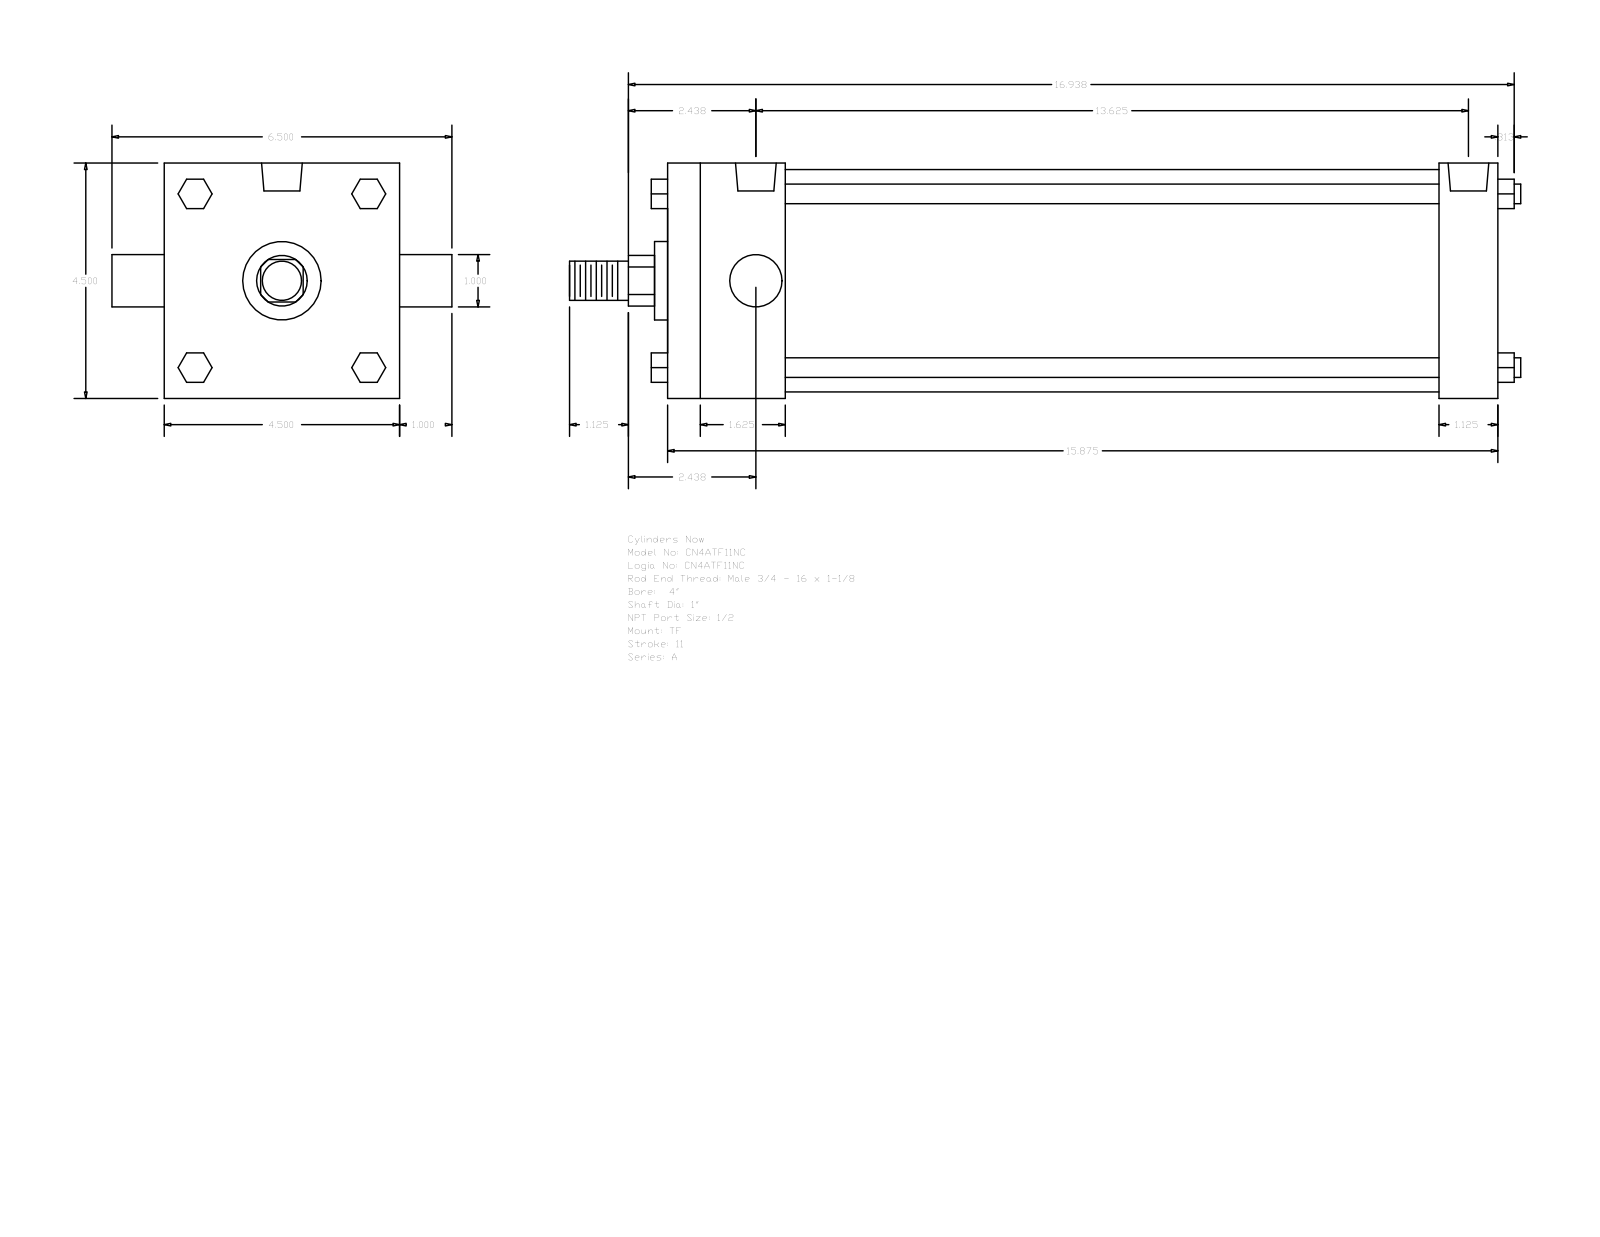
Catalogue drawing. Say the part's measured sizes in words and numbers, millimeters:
The part is named "A_TF__0400_1". Its 3-D file was written by "GSSL Pune (CONFIG_CONTROL_DESIGN)". It is 0 solids with 120 faces: 92 planar, 28 cylindrical and 0 other. Overall it measures 461.96 by 165.1 by 114.3 millimeters. Round holes: 3 of diameter 8.73, 2 of diameter 19.77. Round bosses or shafts: 4 of diameter 9.53, 2 of diameter 25.4, 1 of diameter 107.95, 1 of diameter 38.1, 1 of diameter 19.05. Partial cylindrical surfaces (rounded edges, fillets, slot ends): 1 of radius 12.29. The main face-to-face distances are 114.3, 403.22, 28.57, 374.65, 57.15, 317.5, 346.07, 14.29, 42.16, 73.03. The hole center spacings are 3.18, 342.9, 339.72, 346.08.
